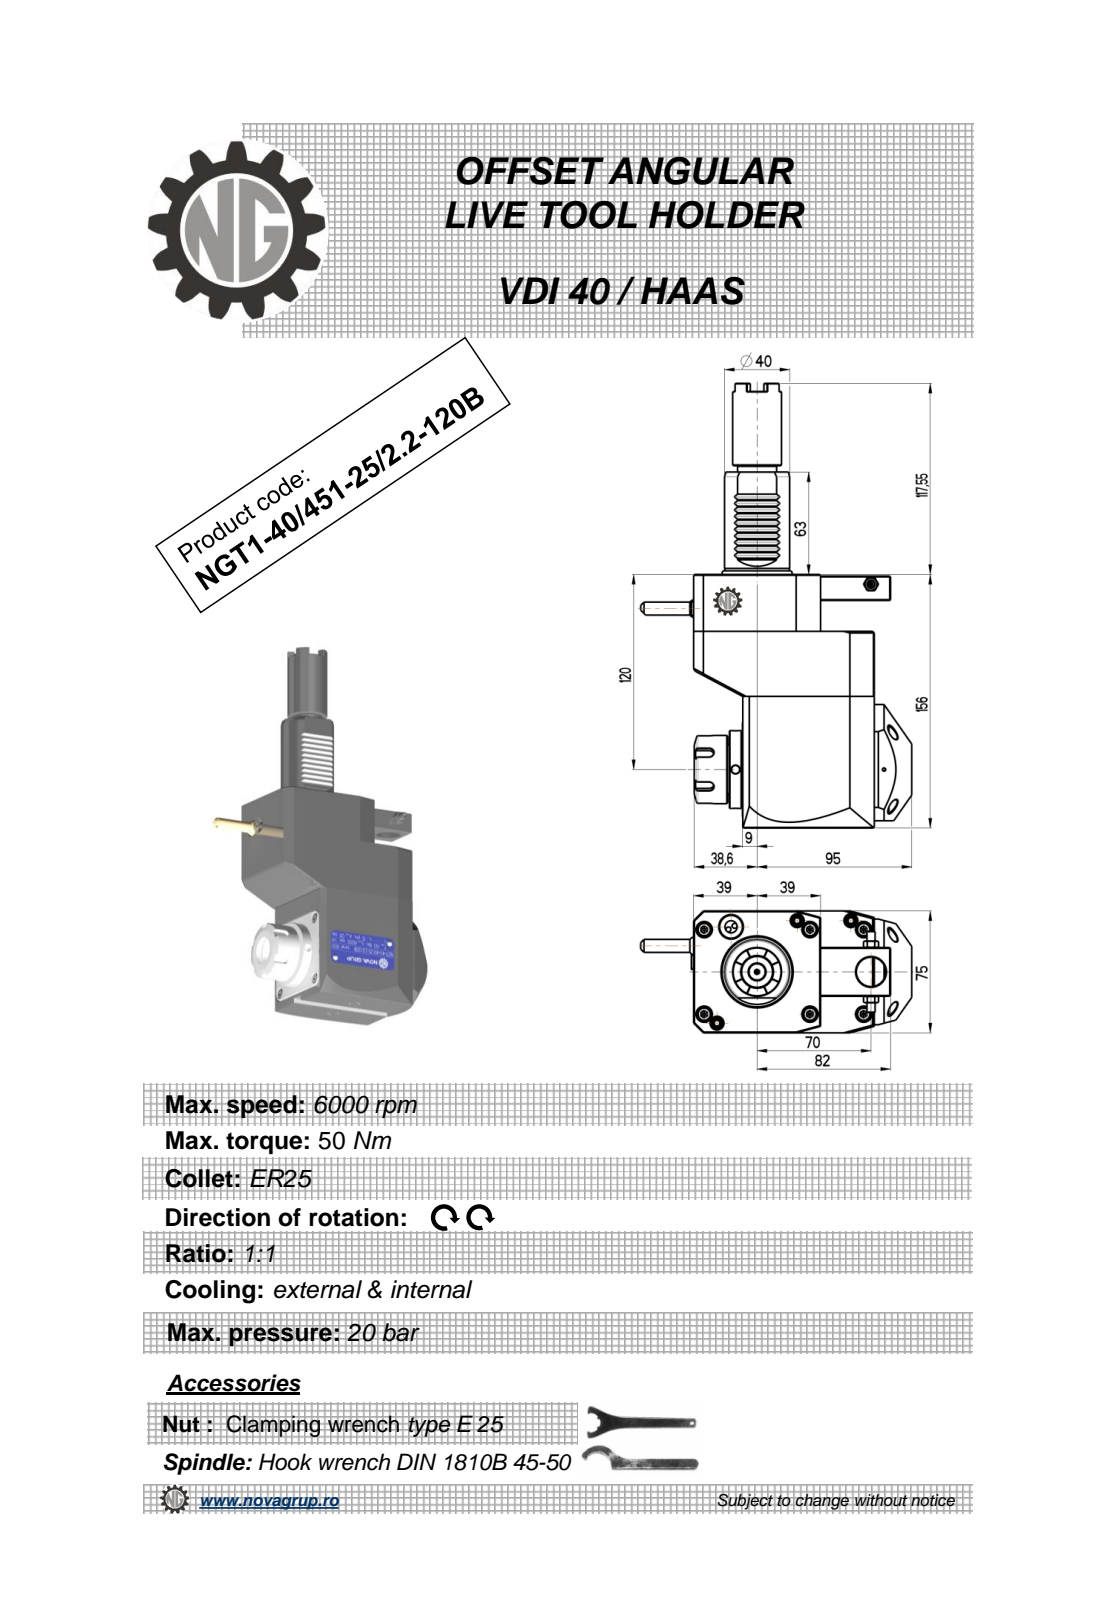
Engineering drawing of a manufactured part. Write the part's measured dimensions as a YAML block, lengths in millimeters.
part_name: "NGT1_40_451_25_2_2_120B"
step_written_by: "PRO/ENGINEER BY PARAMETRIC TECHNOLOGY CORPORATION, 2010280 (CONFIG_CONTROL_DESIGN)"
units: millimeters
bodies: {solids: 1, faces: 487, planar: 231, cylindrical: 97, other: 159}
overall_size: [273.55, 166.5, 76.6]
volume: 1226000
surface_area: 94708
round_holes:
  - {diameter: 5, count: 3}
  - {diameter: 3, count: 1}
  - {diameter: 4.2, count: 1}
  - {diameter: 9.5, count: 1}
  - {diameter: 18, count: 1}
  - {diameter: 20.3, count: 1}
  - {diameter: 26.8, count: 1}
round_bosses_or_shafts:
  - {diameter: 48, count: 1}
  - {diameter: 42, count: 1}
  - {diameter: 40, count: 1}
  - {diameter: 37.5, count: 1}
  - {diameter: 33, count: 1}
  - {diameter: 30, count: 1}
  - {diameter: 26.58, count: 1}
  - {diameter: 24, count: 1}
partial_cylinders:
  - {radius: 0.26, count: 12}
  - {radius: 0.3, count: 10}
  - {radius: 0.2, count: 6}
  - {radius: 3, count: 5}
  - {radius: 0.5, count: 1}
  - {radius: 9.75, count: 1}
  - {radius: 40, count: 1}
face_to_face_distances: [75, 156, 111, 30, 121, 35, 81, 33, 78, 48]
hole_center_spacings: [13.25, 20.93, 70, 83.25, 100.28, 112.5, 141.16]
